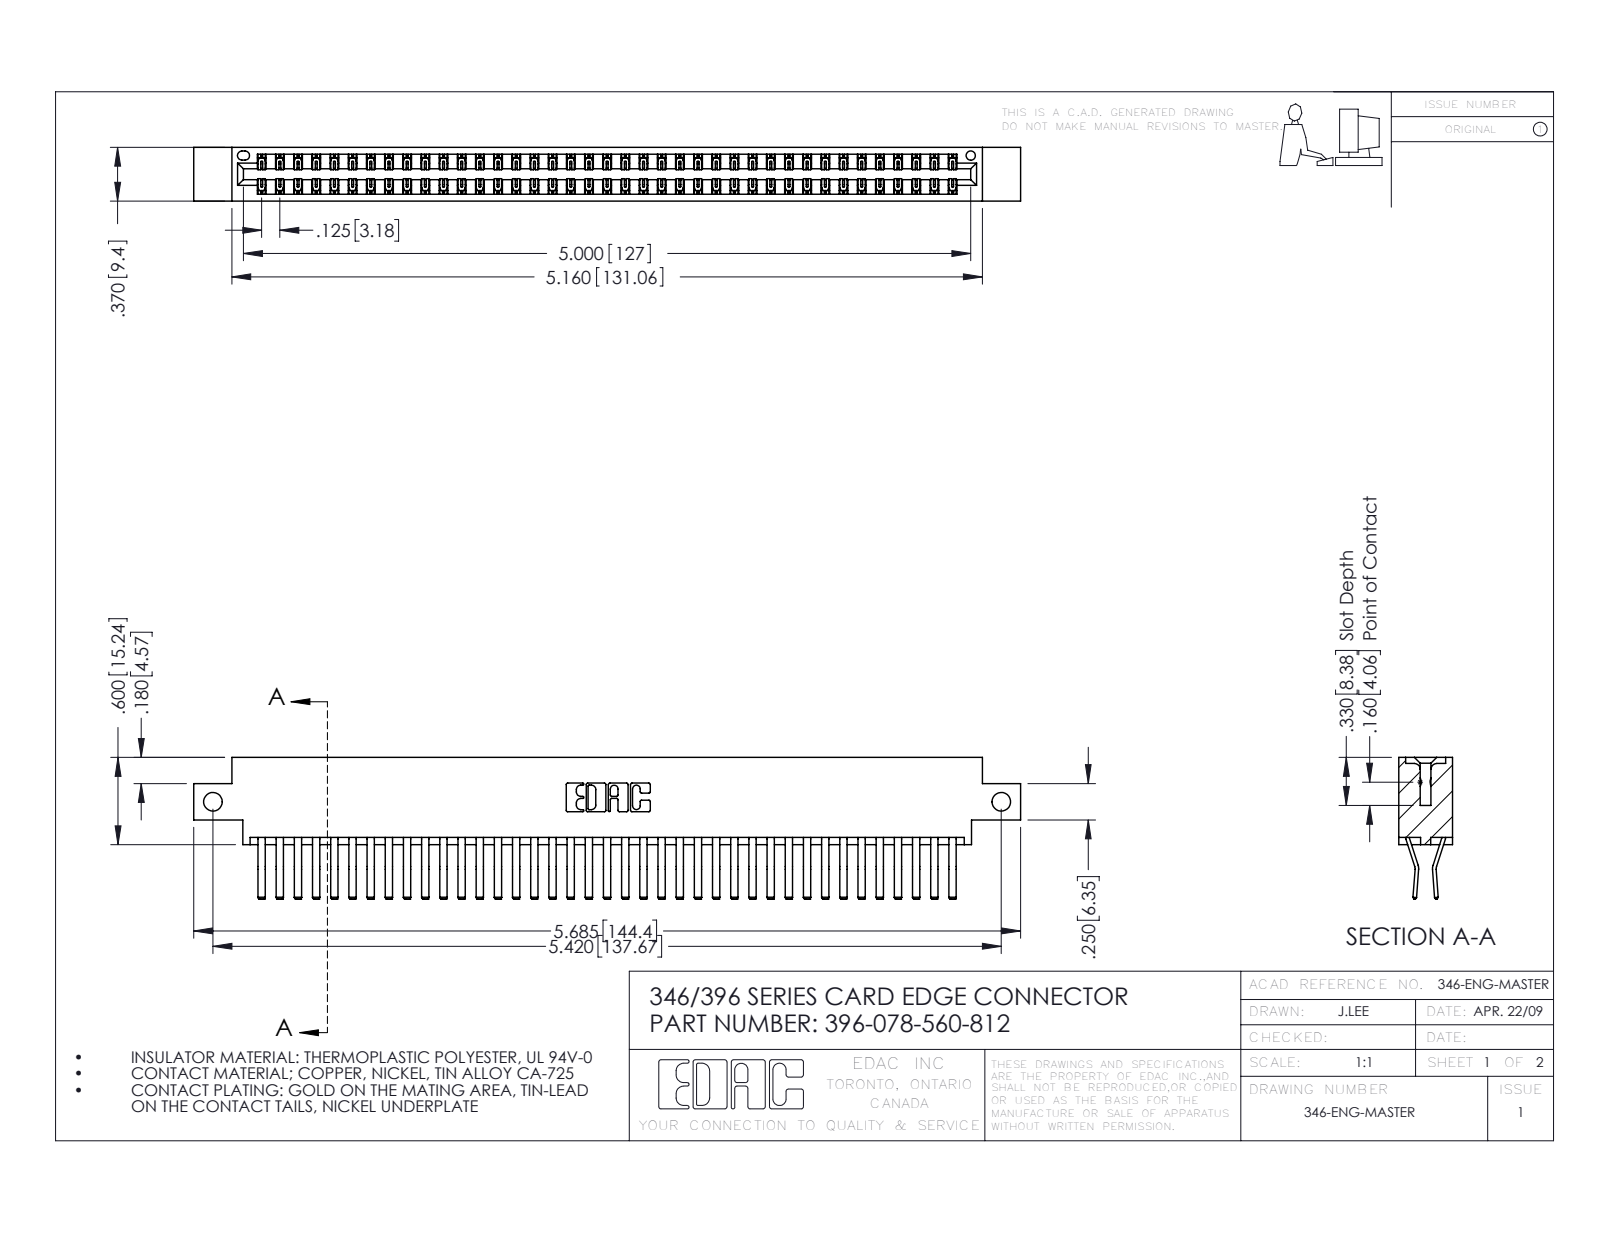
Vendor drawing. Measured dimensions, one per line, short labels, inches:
name: 396-078-560-812; 345-292-001_560 Tail; 346 Part_0.170 Offset - Side Mount
written by: SolidWorks 2016 (CONFIG_CONTROL_DESIGN)
unit: in
bodies: 79 solids, 4338 faces (2810 planar, 1528 cylindrical, 0 other)
size: 5.685 × 0.975 × 0.37
volume: 0.874 in³; area: 32.63 in²
holes: 2× ⌀0.128, 1× ⌀0.064
rounds: 117× R0.006, 22× R0.01, 6× R0.007, 6× R0.031, 3× R0.026, 2× R0.01, 2× R0.014, 2× R0.022
face distances: 0.048, 0.322, 0.37, 0.025, 0.25, 0.072, 0.298, 0.275, 0.148, 0.222
hole spacings: 5.42
